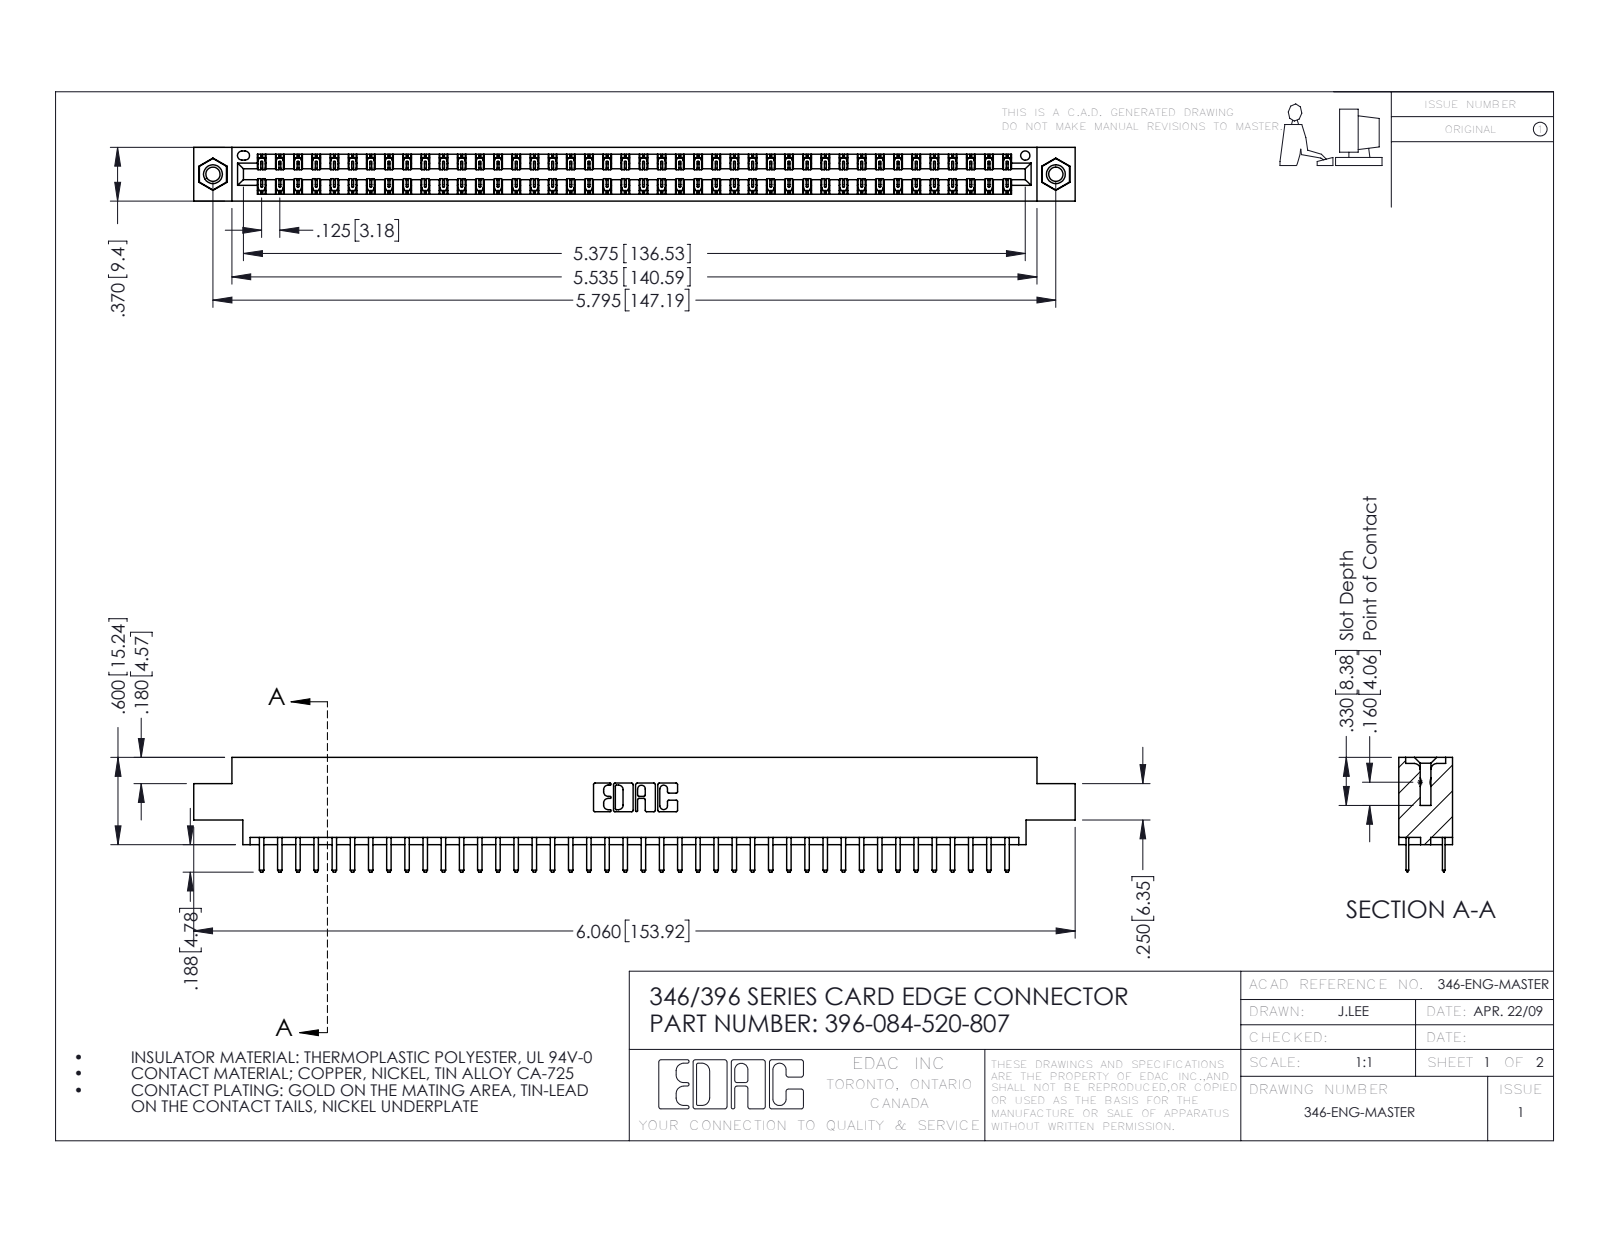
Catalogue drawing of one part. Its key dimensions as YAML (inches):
part_name: "346 Part_0.170 Offset - 0.156 Dia-TI; 345-292-001_345-293-120; 396-084-520-807; 345-250-001_345-250-005-103"
step_written_by: "SolidWorks 2016 (CONFIG_CONTROL_DESIGN)"
units: inches
bodies: {solids: 87, faces: 4890, planar: 3220, cylindrical: 1654, other: 16}
overall_size: [6.06, 0.788, 0.37]
volume: 0.903
surface_area: 31.74
round_holes:
  - {diameter: 0.098, count: 2}
  - {diameter: 0.125, count: 2}
  - {diameter: 0.156, count: 2}
  - {diameter: 0.064, count: 1}
round_bosses_or_shafts:
  - {diameter: 0.155, count: 2}
partial_cylinders:
  - {radius: 0.006, count: 126}
  - {radius: 0.01, count: 88}
  - {radius: 0.01, count: 22}
  - {radius: 0.007, count: 6}
  - {radius: 0.031, count: 6}
  - {radius: 0.026, count: 3}
  - {radius: 0.014, count: 2}
  - {radius: 0.022, count: 2}
face_to_face_distances: [0.048, 0.322, 0.25, 0.37, 0.275, 0.072, 0.298, 0.025, 0.222, 0.148]
hole_center_spacings: [0.246, 5.586, 5.795]
